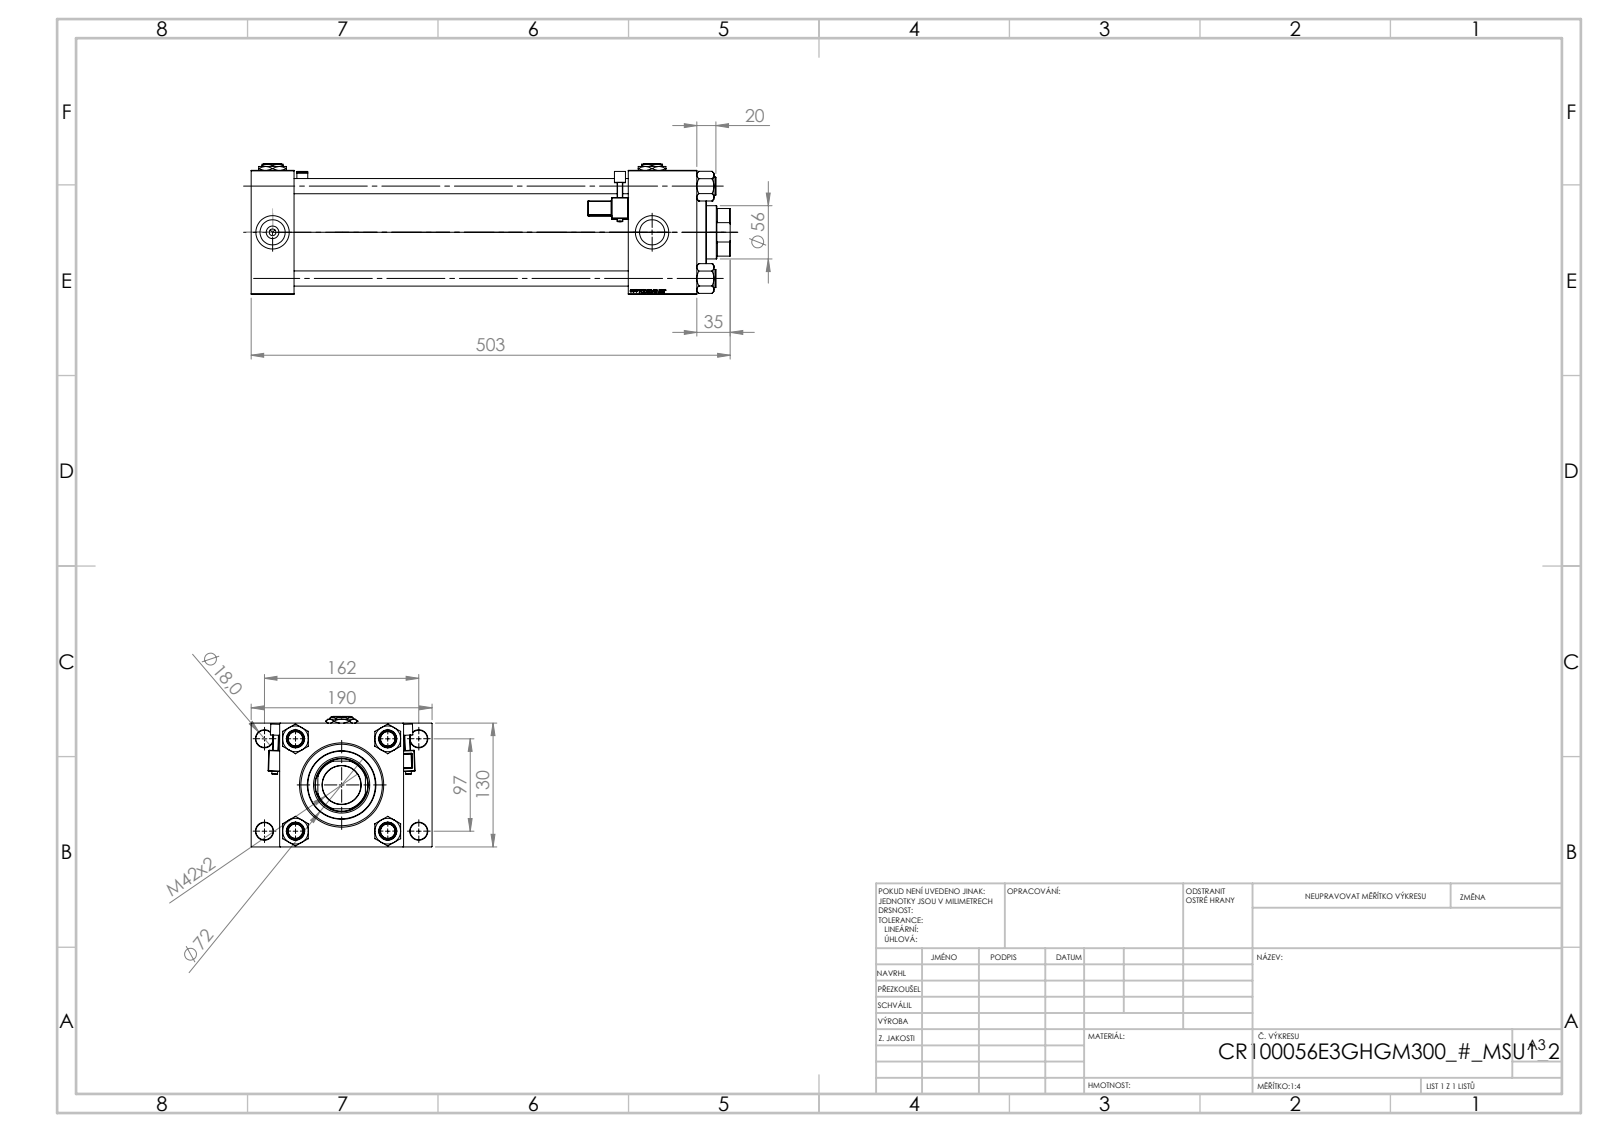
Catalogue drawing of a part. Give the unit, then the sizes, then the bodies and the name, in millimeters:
Units: millimetres
Overall size (bounding box): 503 × 190 × 137
Round holes (diameter × count): ⌀16 ×4, ⌀18 ×4, ⌀26.44 ×4, ⌀35 ×4, ⌀7 ×3, ⌀2.5 ×2, ⌀40.5 ×1, ⌀56 ×1, ⌀59 ×1, ⌀76 ×1, ⌀85.5 ×1, ⌀100 ×1
Round bosses / shafts (diameter × count): ⌀19 ×4, ⌀6 ×2, ⌀106 ×1, ⌀72 ×1
Partial cylindrical surfaces — rounded edges, fillets, slot ends (radius × count): R0.5 ×48, R1 ×2, R2.5 ×2, R4 ×2, R27 ×1
Main face-to-face distances: 130, 45, 468, 423, 30, 396, 351, 72, 160, 96
Hole centre spacings: 32.55, 49.02, 62.87, 68.52, 94.41, 96.9, 101.73, 102.27
Volume: 4 008 000 mm³ · Surface area: 683 588 mm²
Bodies: 15 solids, 1444 faces (653 planar, 161 cylindrical, 630 other)
Part name (STEP PRODUCT): V215CR_E_Body; V215CR_TYCINKA_E; V215_VC_A; NUT_M5_E (+3 more)
STEP written by: SolidWorks 2019 (CONFIG_CONTROL_DESIGN)
